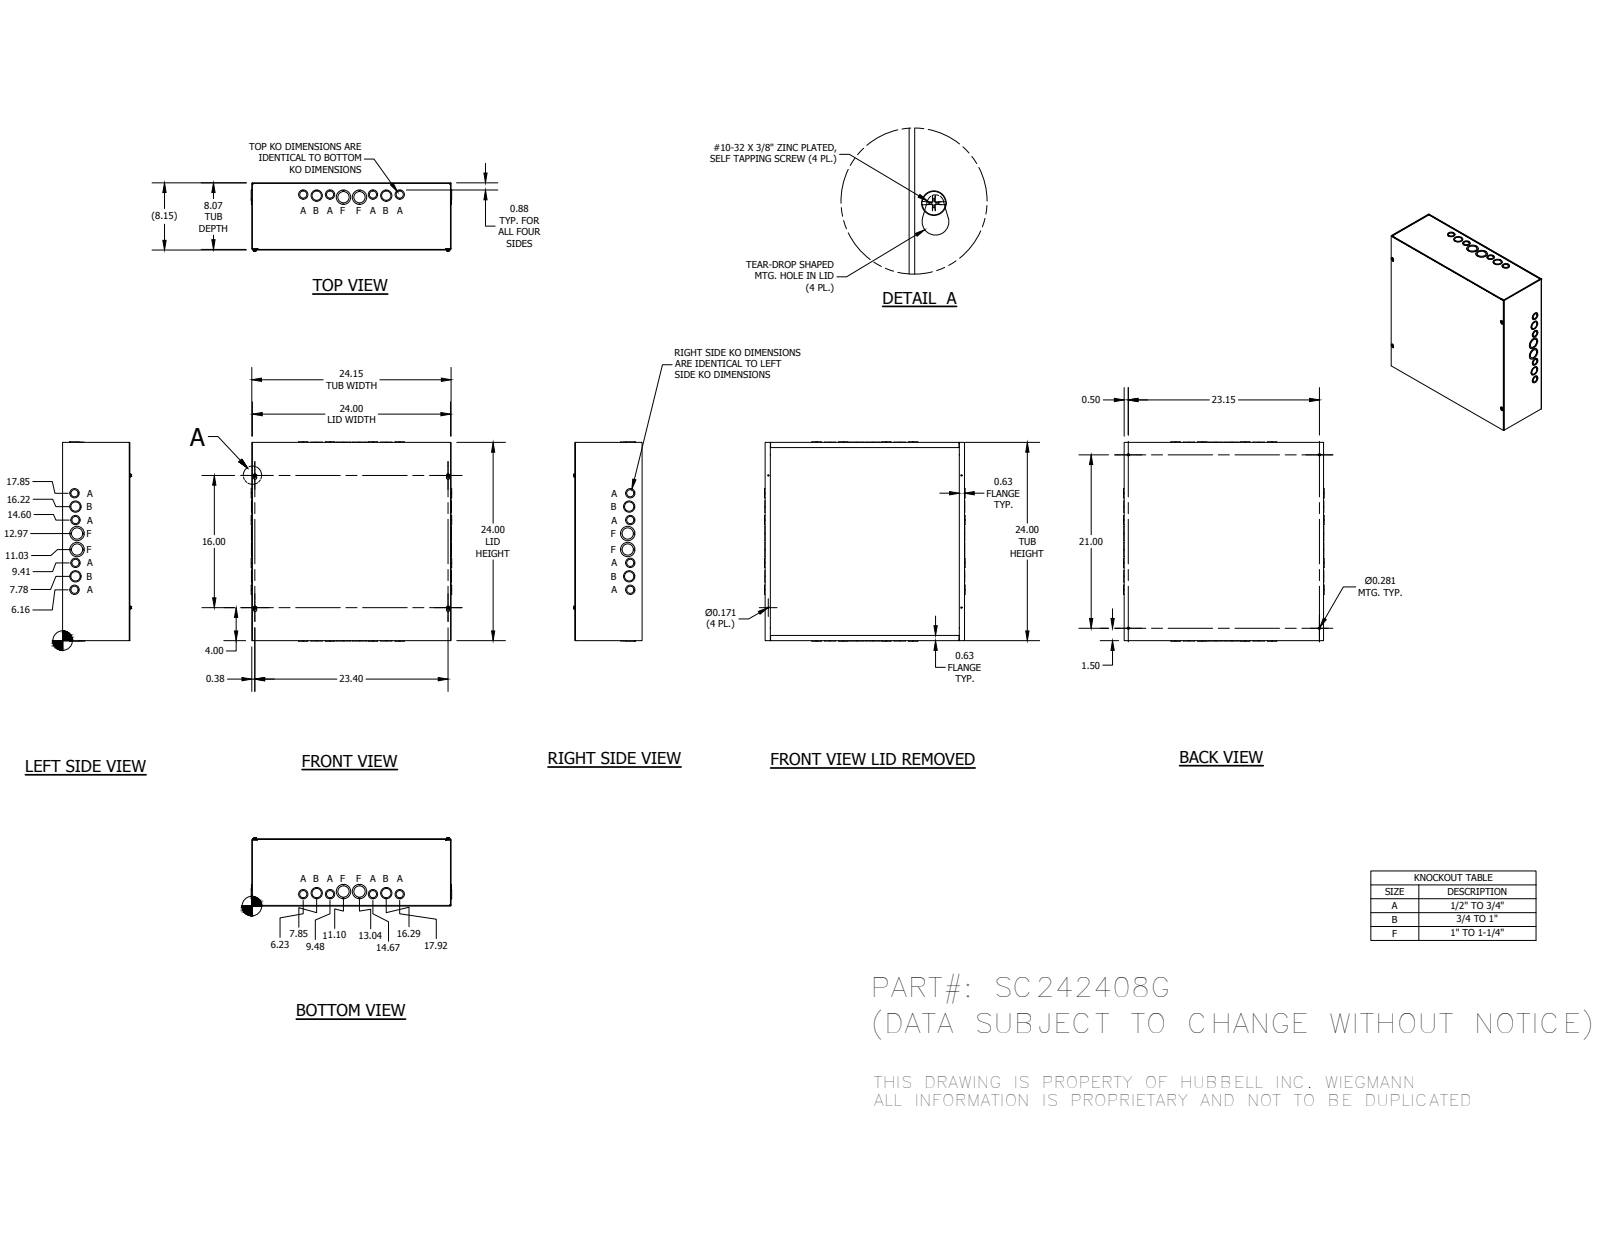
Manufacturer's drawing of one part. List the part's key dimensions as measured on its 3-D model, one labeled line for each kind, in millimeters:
Part name (STEP PRODUCT): SC242408GBLR; SC2408GTB; SC2424GLPA; 37214 (+1 more)
STEP written by: Autodesk Inventor 2014 (AUTOMOTIVE_DESIGN)
Units: millimetres
Bodies: 37 solids, 1219 faces (899 planar, 236 cylindrical, 84 other)
Overall size (bounding box): 617.12 × 613.36 × 210.31
Round holes (diameter × count): ⌀28.57 ×14, ⌀22.22 ×10, ⌀34.92 ×8, ⌀4.34 ×4, ⌀7.14 ×4, ⌀44.45 ×4
Round bosses / shafts (diameter × count): ⌀4.83 ×4
Partial cylindrical surfaces — rounded edges, fillets, slot ends (radius × count): R0.4 ×12, R2.28 ×12, R3.17 ×4, R5.16 ×4
Main face-to-face distances: 1.88, 205.08, 203.2, 206.96, 609.6, 611.48, 607.72, 613.36, 605.84, 3.76
Hole centre spacings: 41.39, 41.4, 42.03, 63.58, 82.55, 82.69, 90.9, 124.07
